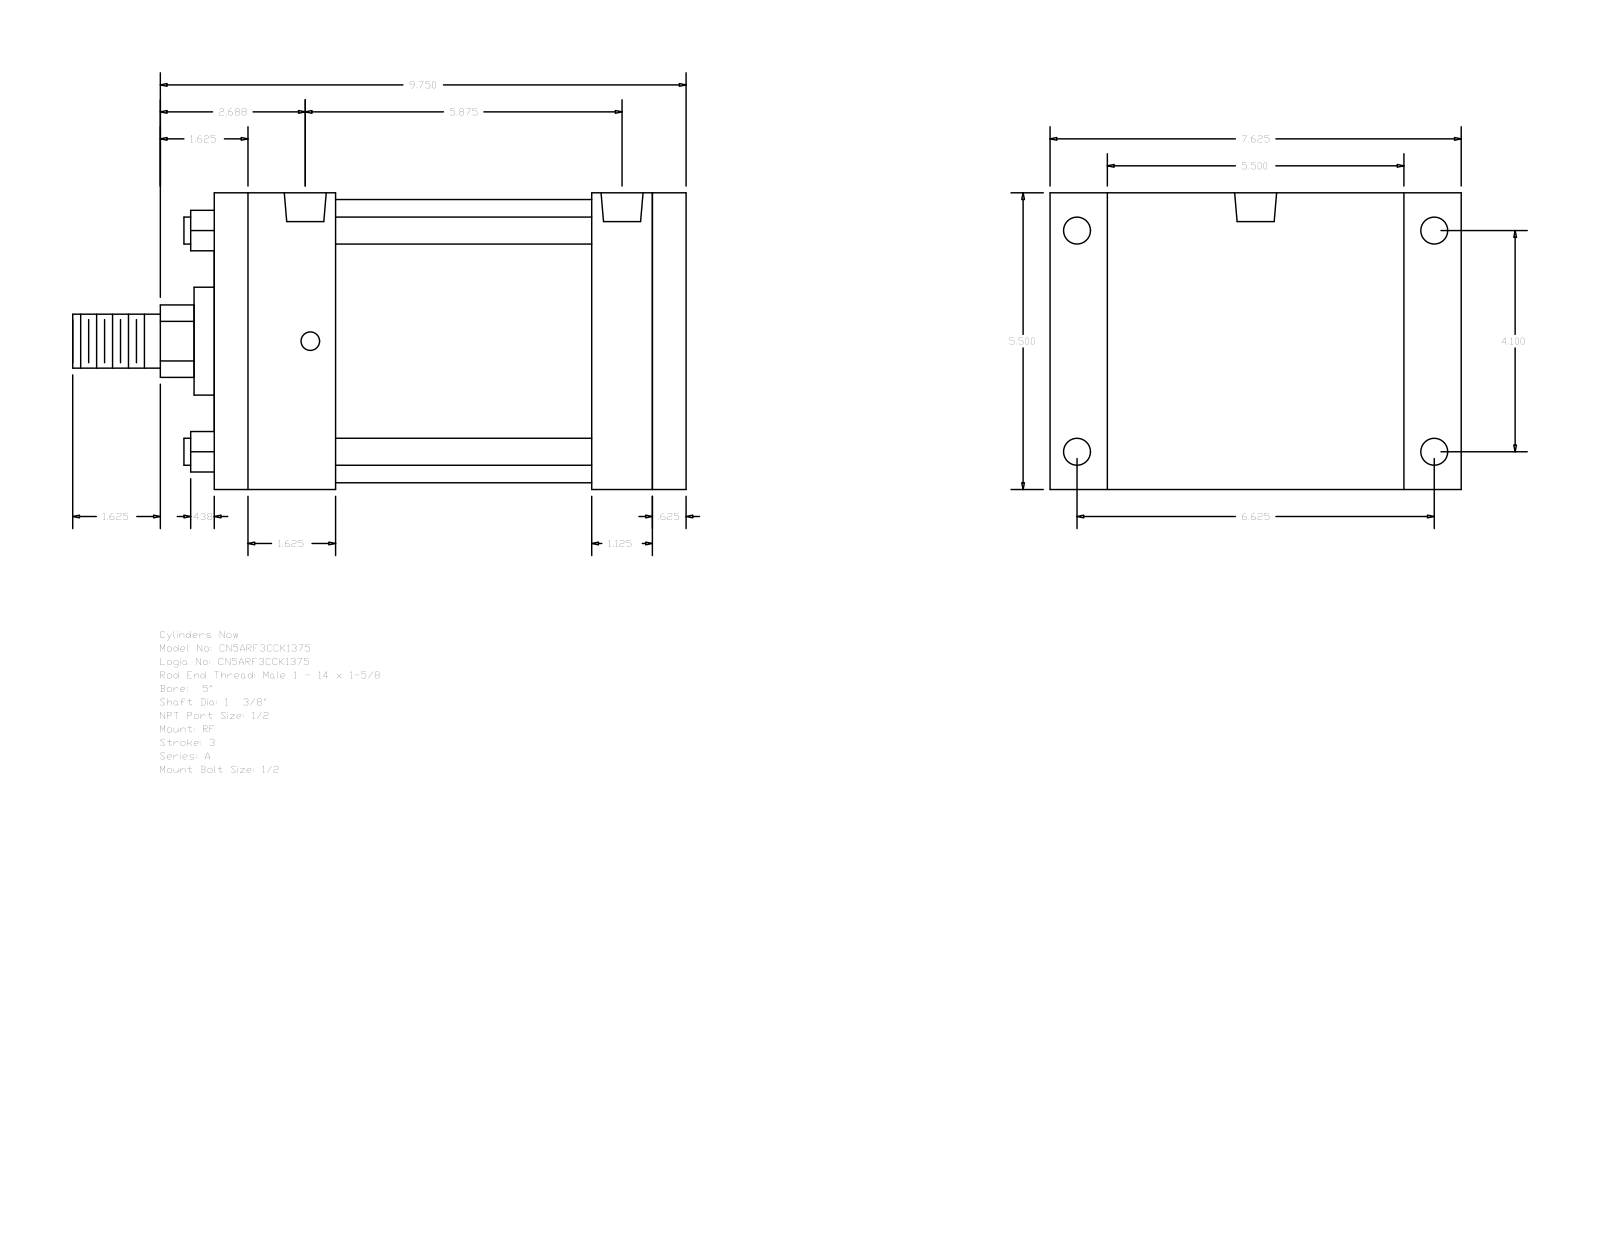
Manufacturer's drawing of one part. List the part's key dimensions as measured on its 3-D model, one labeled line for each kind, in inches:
Part name (STEP PRODUCT): A_RF__0500_1.375
STEP written by: GSSL Pune (CONFIG_CONTROL_DESIGN)
Units: inches
Bodies: 0 solids, 92 faces (64 planar, 28 cylindrical, 0 other)
Overall size (bounding box): 11.375 × 7.625 × 5.5
Round holes (diameter × count): ⌀0.344 ×4, ⌀0.5 ×4, ⌀0.778 ×2
Round bosses / shafts (diameter × count): ⌀0.5 ×4, ⌀5.25 ×1, ⌀2 ×1, ⌀1.375 ×1, ⌀1 ×1
Partial cylindrical surfaces — rounded edges, fillets, slot ends (radius × count): R0.672 ×1
Main face-to-face distances: 5.5, 8.75, 8.125, 0.625, 2.25, 1.125, 5.875, 6.5, 7, 4.75
Hole centre spacings: 0.094, 4.1, 5.687, 5.781, 6.625, 7.791, 5.875
